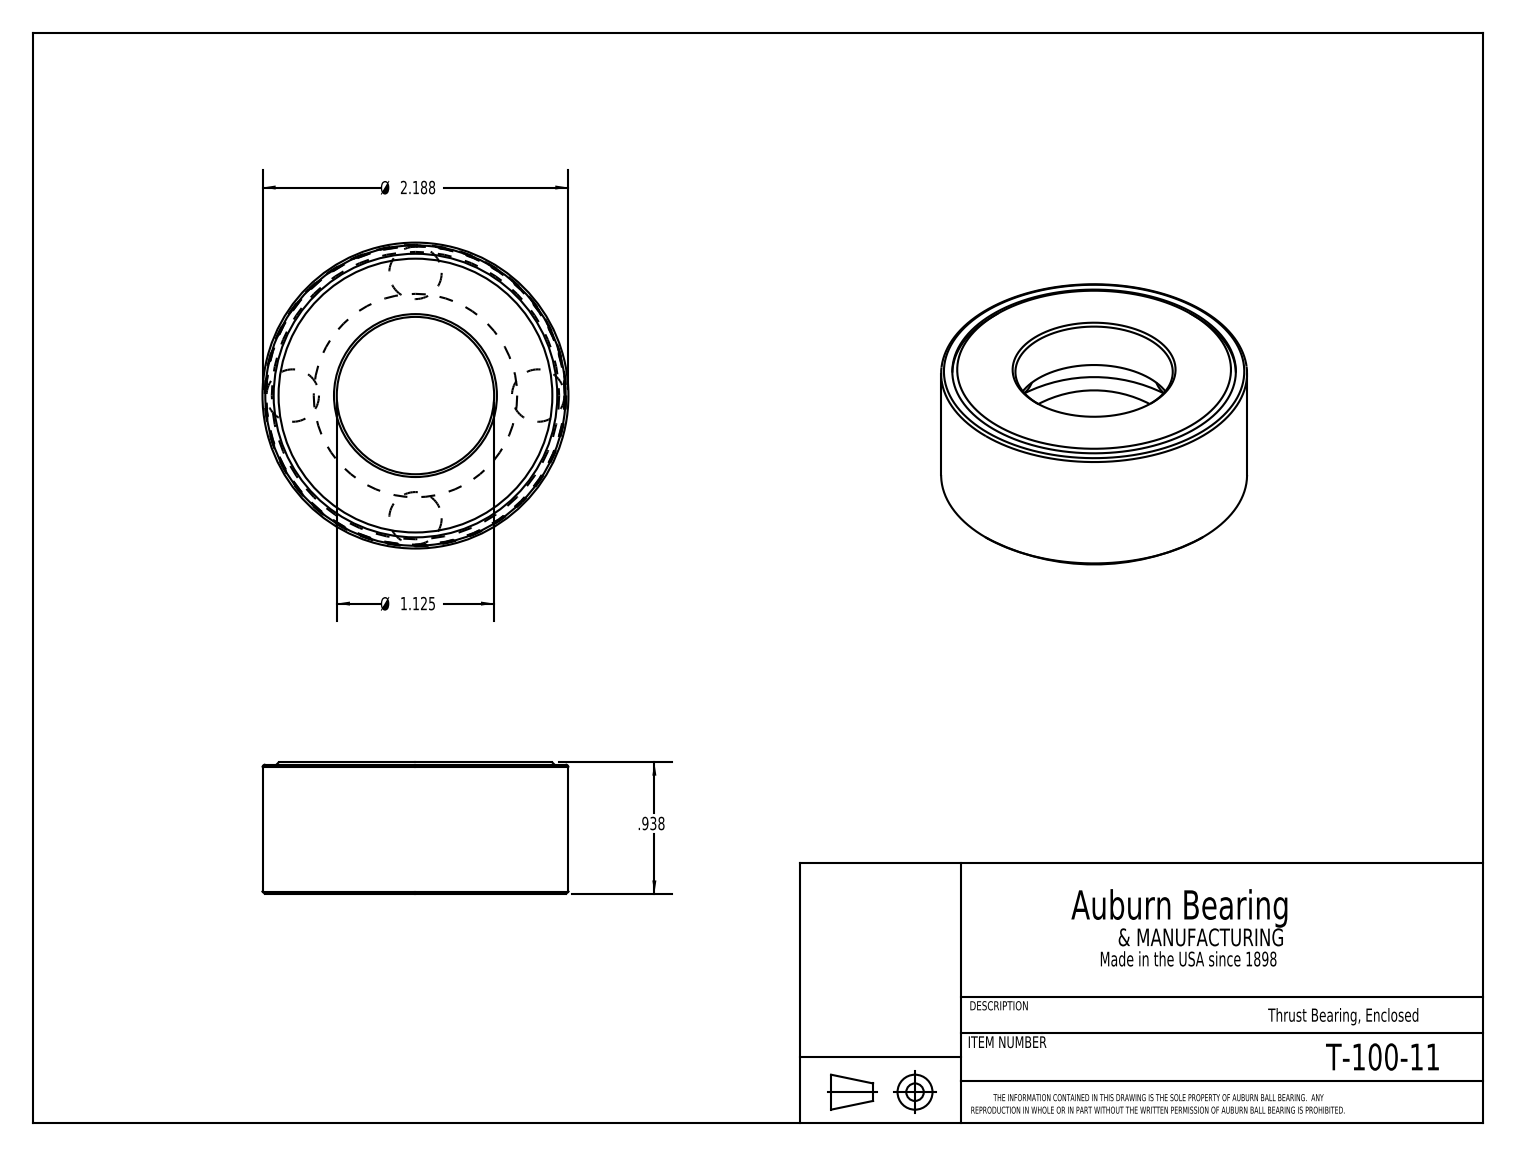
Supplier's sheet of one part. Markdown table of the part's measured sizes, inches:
| quantity | value |
| --- | --- |
| part name | T-100-11 |
| STEP written by | SolidWorks 2016 (CONFIG_CONTROL_DESIGN) |
| units | inches |
| bodies | 6 solids, 28 faces (9 planar, 7 cylindrical, 12 other) |
| overall size | 2.188 × 2.188 × 0.938 |
| volume | 1.898 in³ |
| surface area | 28.32 in² |
| round holes (diameter × count) | 1.125 × 1, 1.125 × 1, 2.027 × 1, 2.147 × 1 |
| round bosses / shafts (diameter × count) | 2.187 × 1, 2.133 × 1 |
| main face-to-face distances | 0.937, 0.356, 0.581, 0.225, 0.922, 0.566, 0.341, 0.015, 0.902, 0.546 |
